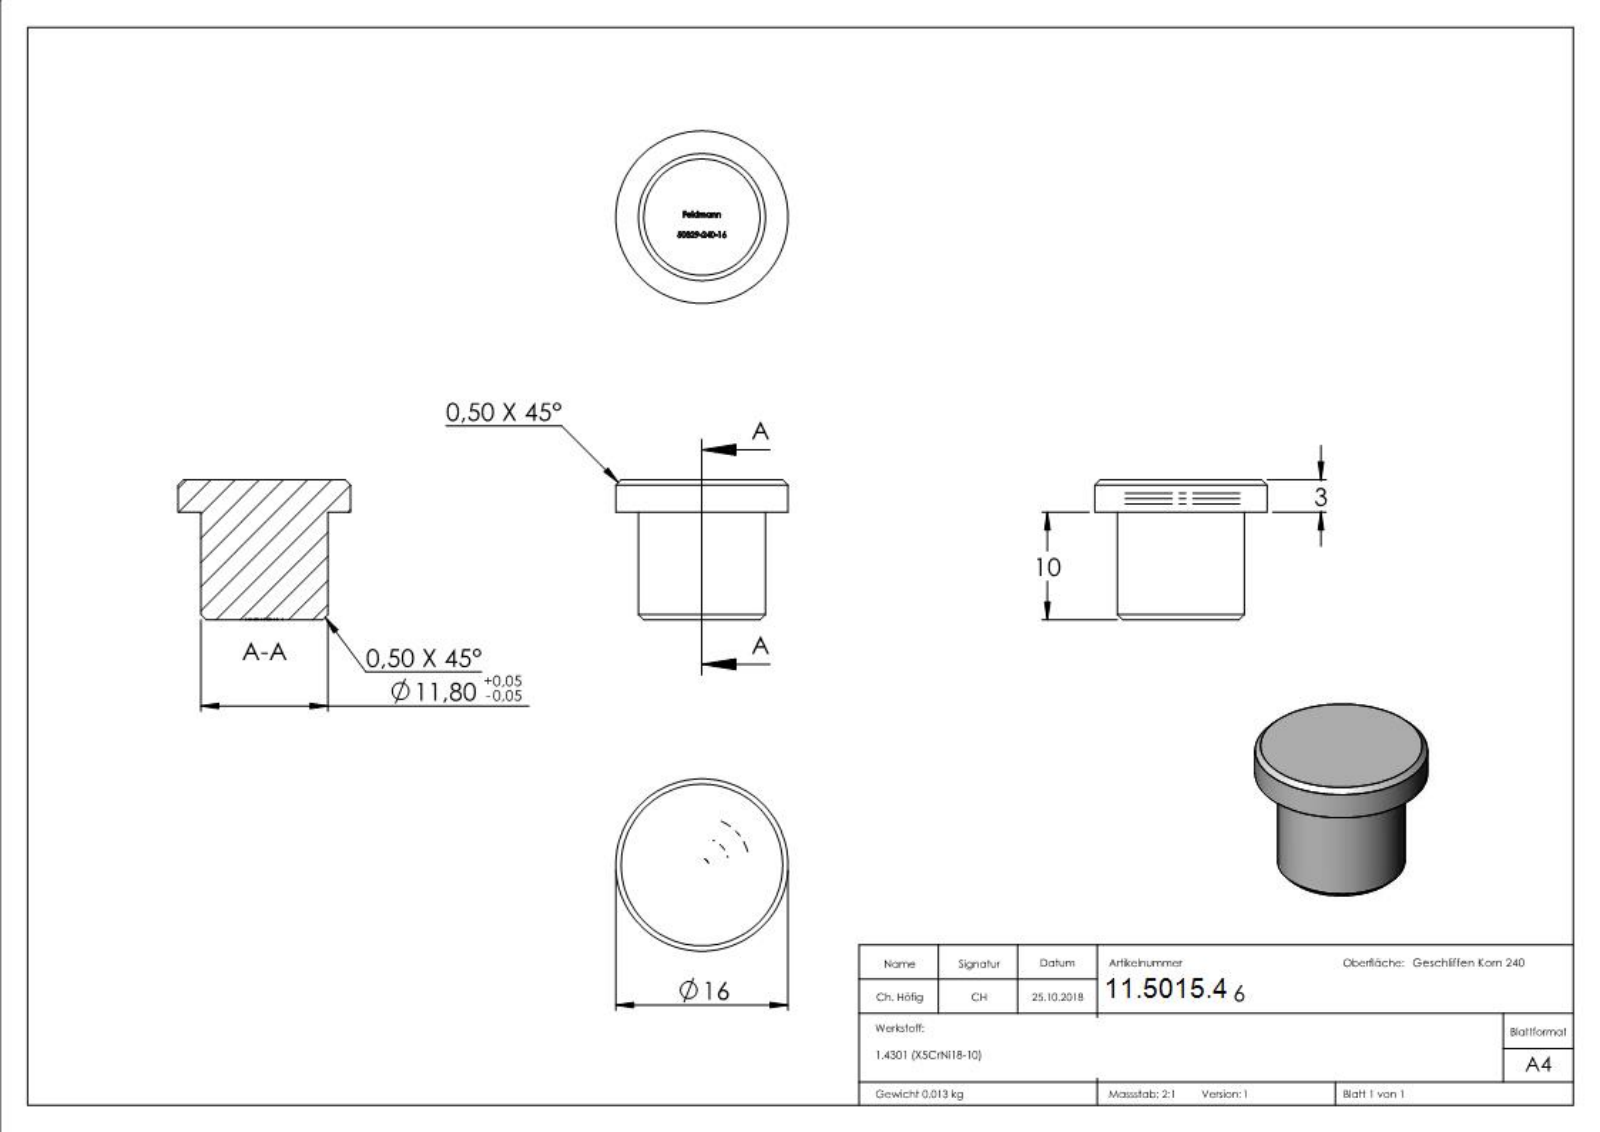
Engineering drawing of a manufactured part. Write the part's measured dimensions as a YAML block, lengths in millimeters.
part_name: "50329-240-16"
step_written_by: "SolidWorks 2015 (CONFIG_CONTROL_DESIGN)"
units: millimeters
bodies: {solids: 1, faces: 265, planar: 139, cylindrical: 4, other: 122}
overall_size: [16, 16, 13]
volume: 1686
surface_area: 902
round_bosses_or_shafts:
  - {diameter: 16, count: 1}
  - {diameter: 11.8, count: 1}
face_to_face_distances: [3, 10, 13, 9.9, 12.9, 0.66, 1.19, 0.71, 1.64, 1.59]
